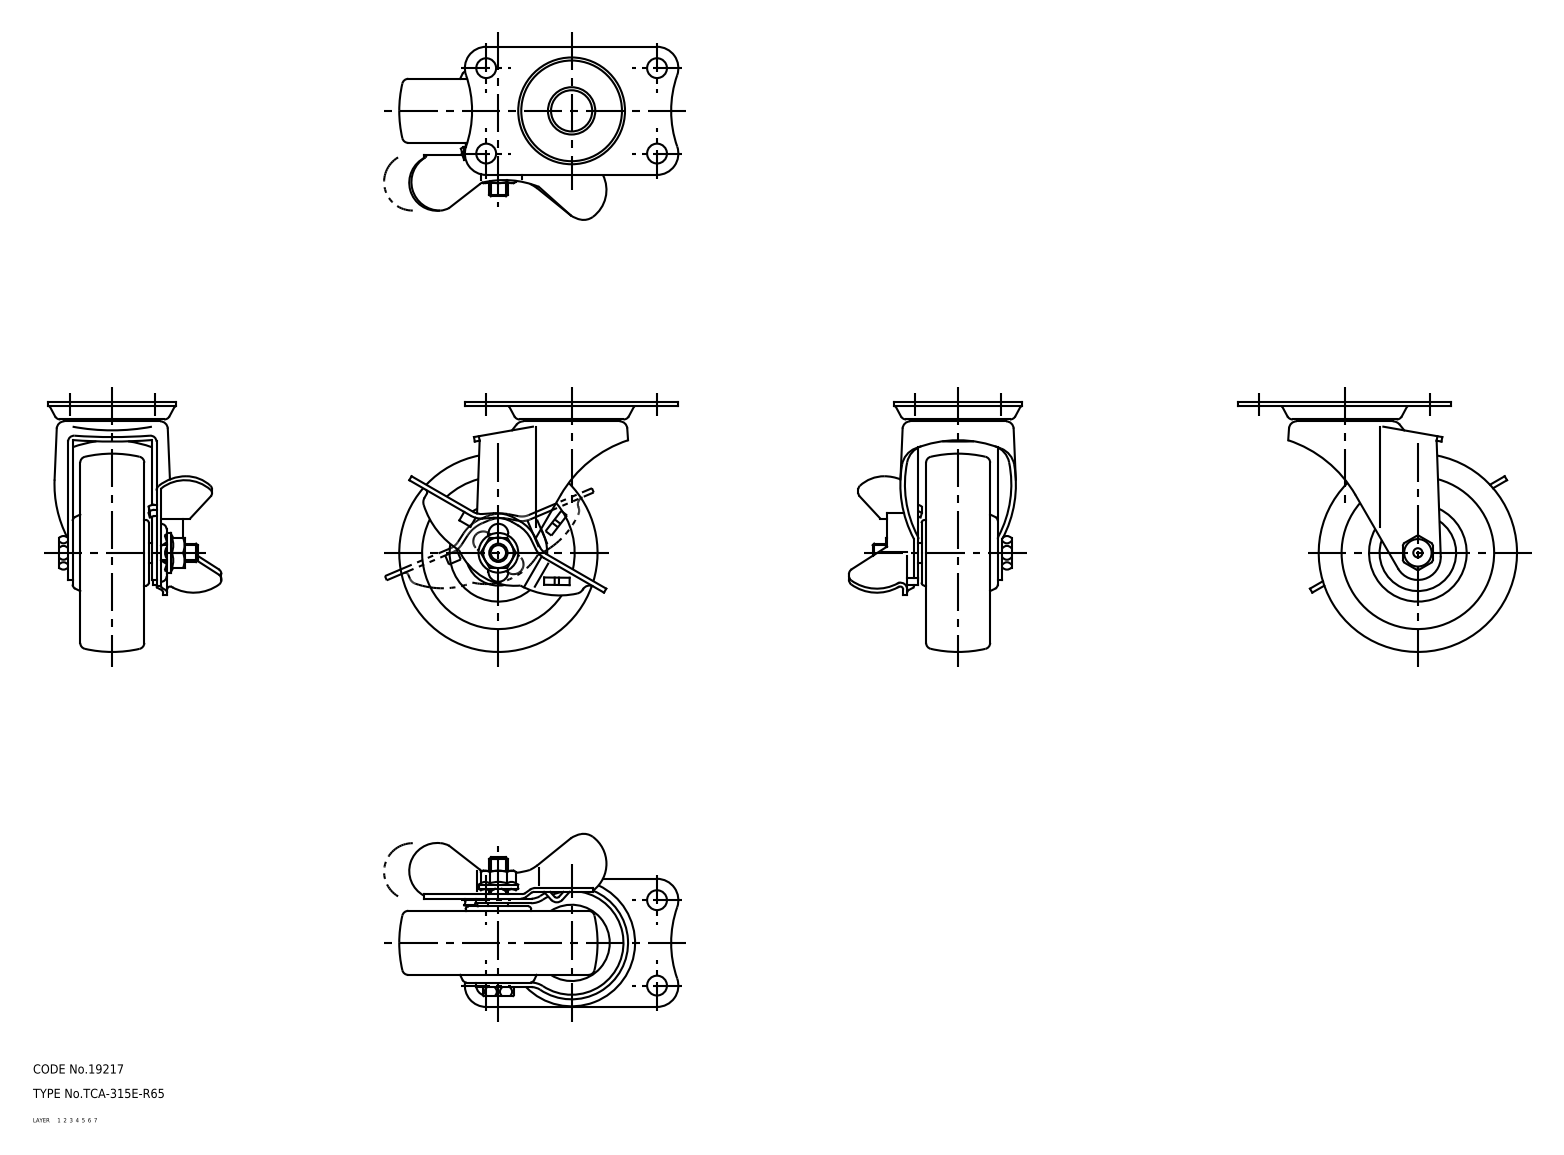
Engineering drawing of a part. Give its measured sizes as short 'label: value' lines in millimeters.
name: axle; wheel; mounting plate; main shaft (+2 more)
written by: CADfix (AUTOMOTIVE_DESIGN)
unit: mm
bodies: 8 solids, 403 faces (0 planar, 0 cylindrical, 403 other)
size: 91.5 × 82 × 56.75
volume: 84 623 mm³; area: 34 299 mm²
